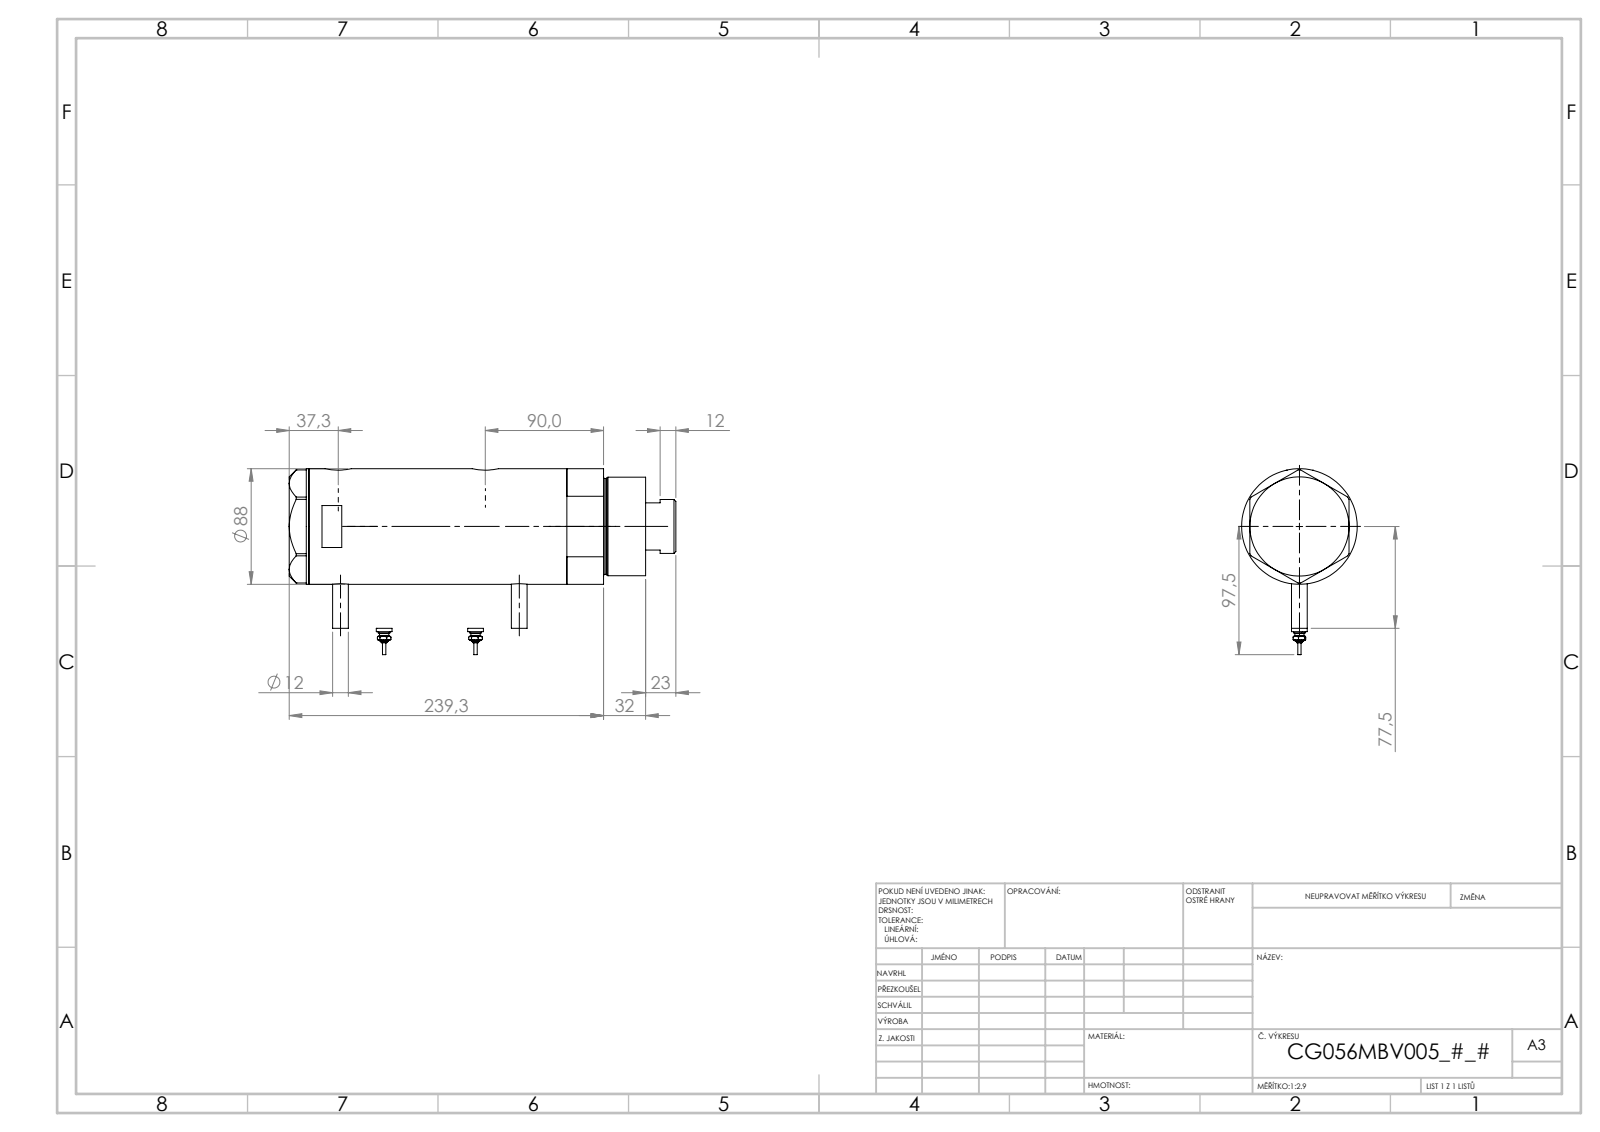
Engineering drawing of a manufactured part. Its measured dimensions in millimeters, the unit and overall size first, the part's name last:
Units: millimetres
Overall size (bounding box): 294.3 × 141.5 × 88
Round holes (diameter × count): ⌀12.5 ×2, ⌀13.16 ×2, ⌀20 ×2, ⌀14.5 ×1, ⌀42 ×1, ⌀43.5 ×1, ⌀56 ×1, ⌀60 ×1, ⌀80 ×1
Round bosses / shafts (diameter × count): ⌀12 ×4, ⌀9 ×2, ⌀7 ×2, ⌀4.5 ×2, ⌀2.5 ×2, ⌀88 ×1, ⌀75 ×1, ⌀73 ×1
Main face-to-face distances: 134.4, 26, 108.4, 15, 41, 149.4, 256.3, 271.3, 230.3, 121.9
Hole centre spacings: 1.7, 25.8, 110.3, 112, 136.1, 137.8
Volume: 1 590 000 mm³ · Surface area: 226 569 mm²
Bodies: 6 solids, 213 faces (80 planar, 69 cylindrical, 64 other)
Part name (STEP PRODUCT): V270CG_FRONT; V270CG_MIDDLE; V270CG_VC; Switch (+1 more)
STEP written by: SolidWorks 2019 (CONFIG_CONTROL_DESIGN)
